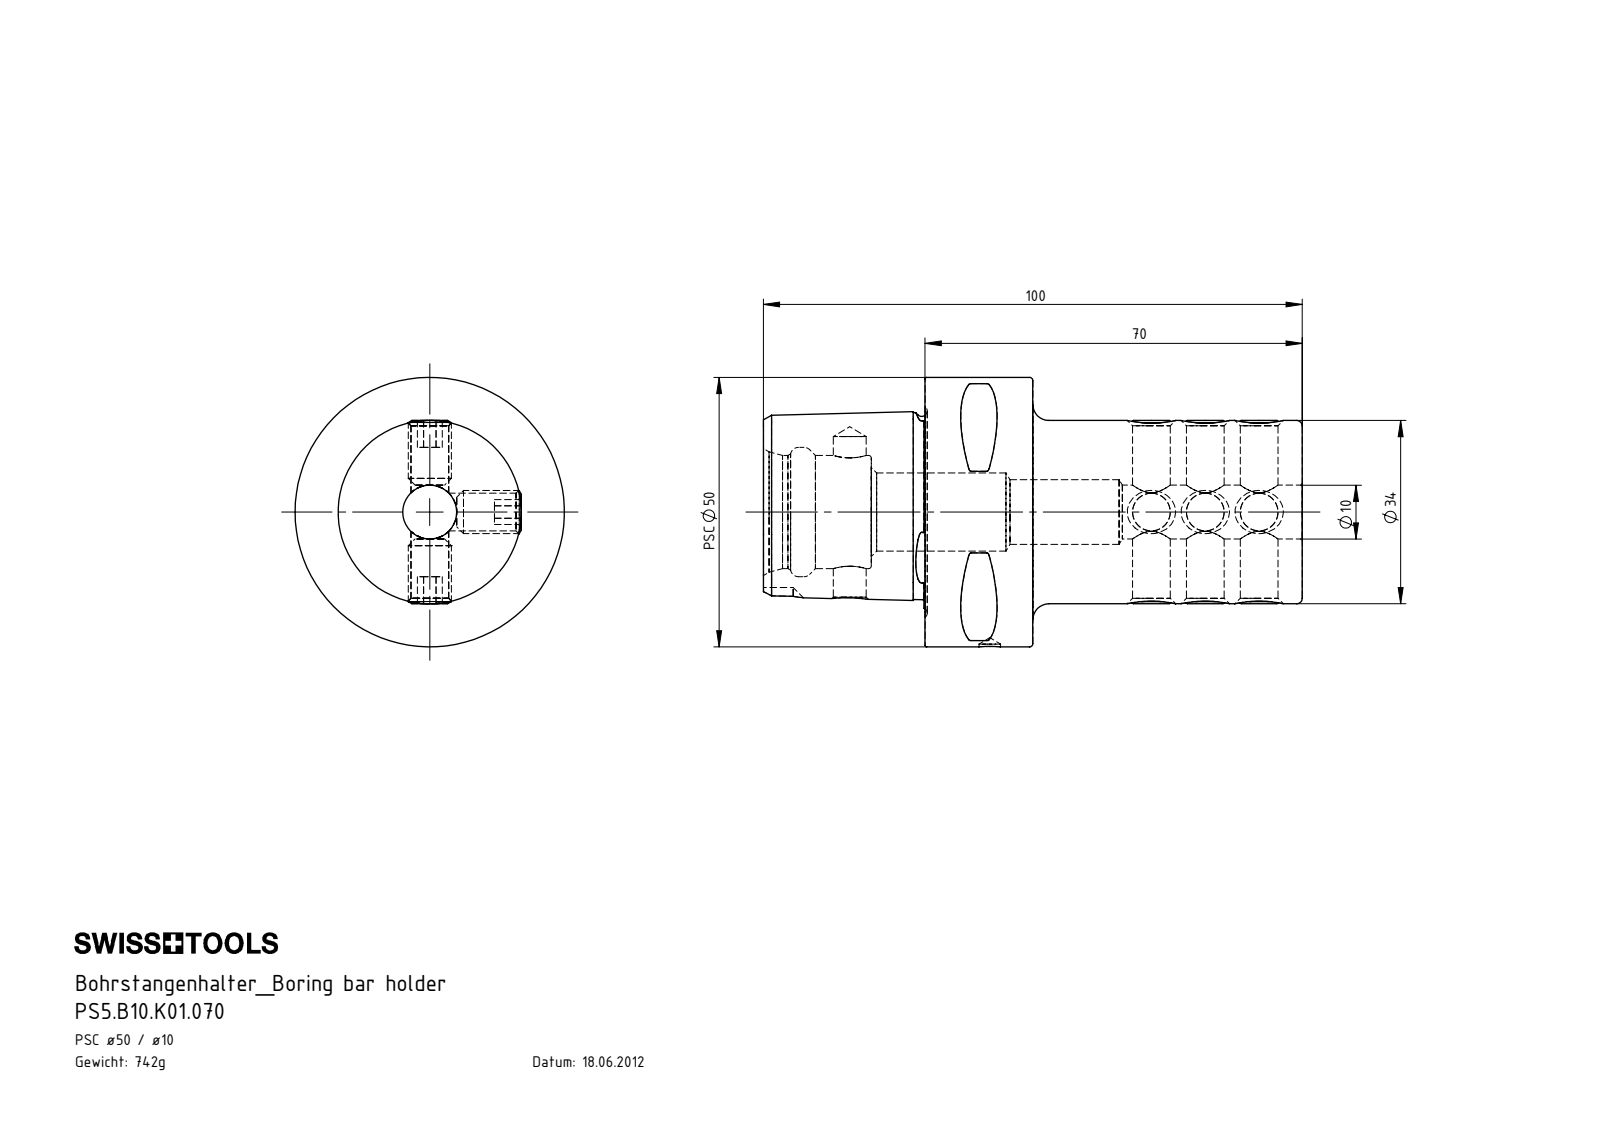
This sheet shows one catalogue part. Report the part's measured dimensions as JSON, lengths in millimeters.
{"part_name": "PS5.B10.K01.070; PS5-B10.K01.070_A; ISO 4026 - M8 x 12_PreviewCfg", "step_written_by": "SolidWorks 2017 (AUTOMOTIVE_DESIGN)", "units": "millimeters", "bodies": {"solids": 10, "faces": 303, "planar": 101, "cylindrical": 67, "other": 135}, "overall_size": [100, 50, 50], "volume_mm3": 94534, "surface_area_mm2": 25432, "round_holes": [[7, 6], [4, 1], [6.1, 1], [10, 1], [12, 1], [14.5, 1], [21, 1], [24, 1]], "round_bosses_or_shafts": [[8, 6], [50, 1], [34, 1]], "partial_cylinders_radius": [[0.5, 8], [4, 1]], "face_to_face_distances": [50, 20, 70, 30, 10, 5, 100, 4, 12, 19.18], "hole_center_spacings": [10, 20, 26, 30, 40, 50, 56, 66]}
